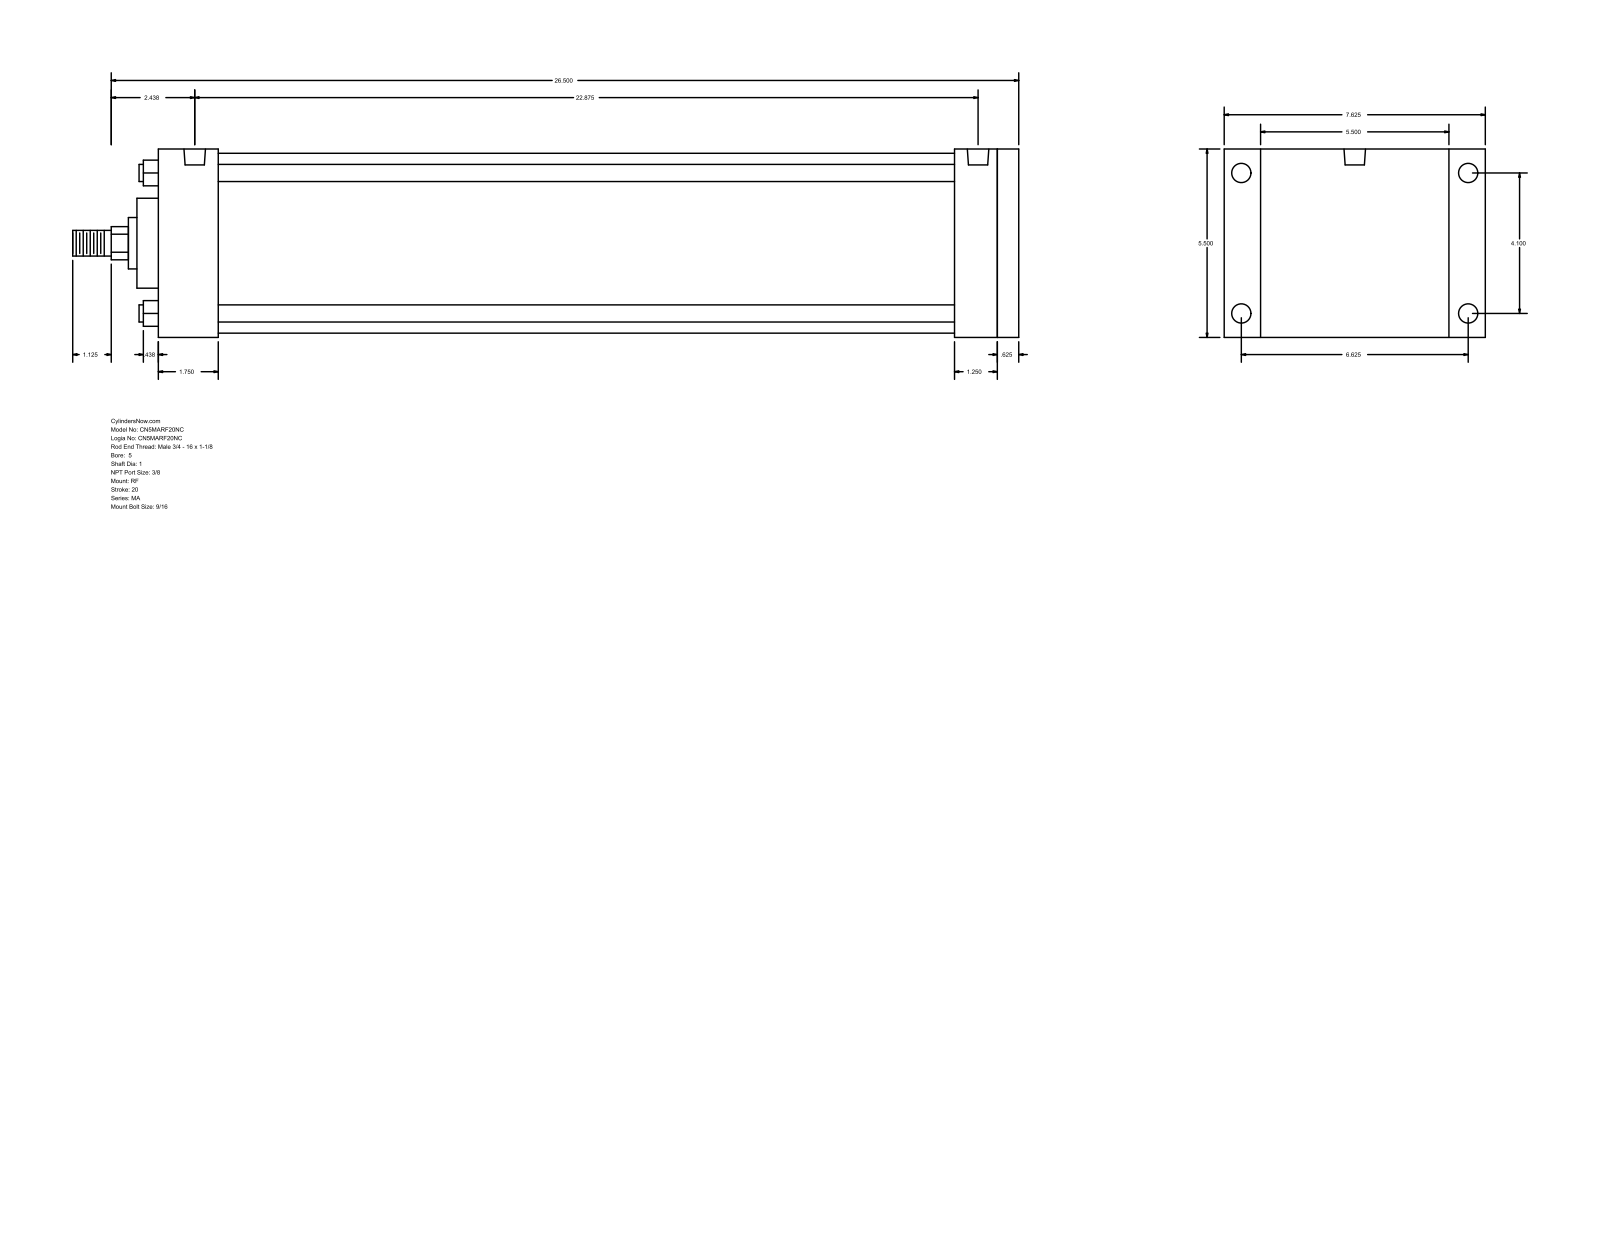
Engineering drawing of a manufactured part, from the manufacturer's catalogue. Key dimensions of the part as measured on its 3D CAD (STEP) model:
Part name (STEP PRODUCT): MA_RF__0500_1
STEP written by: GSSL Pune (CONFIG_CONTROL_DESIGN)
Units: millimetres
Bodies: 0 solids, 94 faces (65 planar, 29 cylindrical, 0 other)
Overall size (bounding box): 701.67 × 193.68 × 139.7
Round holes (diameter × count): ⌀11.11 ×4, ⌀14.29 ×4, ⌀15.93 ×2
Round bosses / shafts (diameter × count): ⌀12.7 ×4, ⌀133.35 ×1, ⌀66.67 ×1, ⌀38.1 ×1, ⌀25.4 ×1, ⌀19.05 ×1
Partial cylindrical surfaces — rounded edges, fillets, slot ends (radius × count): R12.29 ×1
Main face-to-face distances: 139.7, 638.18, 15.87, 622.31, 47.62, 44.46, 577.85, 593.72, 590.56, 546.1
Hole centre spacings: 104.14, 168.28, 197.9, 571.5, 4.76, 4.77, 576.26, 576.27
